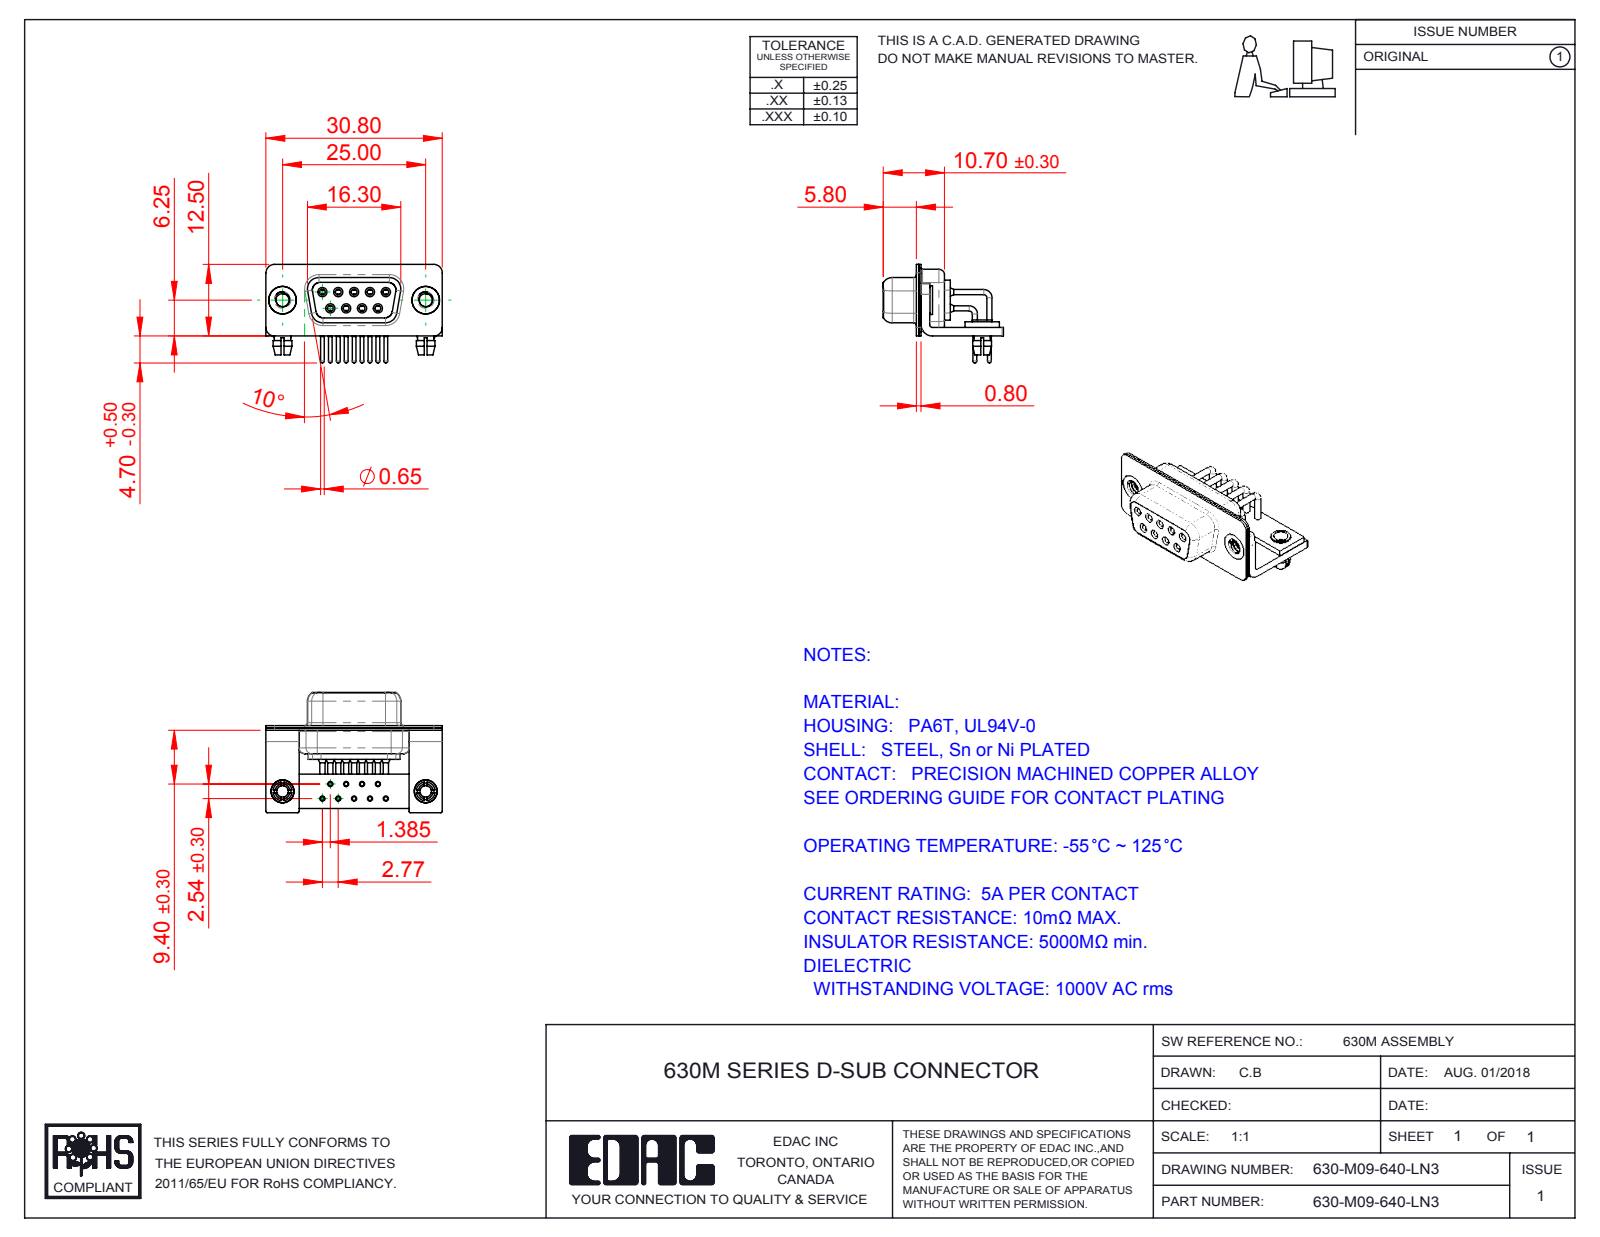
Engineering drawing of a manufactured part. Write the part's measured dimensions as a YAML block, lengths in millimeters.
part_name: "630M Shell Front_09 Contacts; 630M Shell Rear_09 Contacts; 630M Contact Row 1; 630M Contact Row 2 (+6 more)"
step_written_by: "SolidWorks 2016 (CONFIG_CONTROL_DESIGN)"
units: millimeters
bodies: {solids: 19, faces: 916, planar: 276, cylindrical: 416, other: 224}
overall_size: [30.8, 21, 17.2]
volume: 2237
surface_area: 5917
round_holes:
  - {diameter: 2, count: 11}
  - {diameter: 0.9, count: 9}
  - {diameter: 1, count: 9}
  - {diameter: 1.1, count: 9}
  - {diameter: 1.7, count: 9}
  - {diameter: 1.8, count: 9}
  - {diameter: 2.26, count: 2}
  - {diameter: 2.5, count: 2}
  - {diameter: 3.2, count: 2}
  - {diameter: 4, count: 2}
  - {diameter: 4.8, count: 2}
round_bosses_or_shafts:
  - {diameter: 1.6, count: 9}
  - {diameter: 1.5, count: 9}
  - {diameter: 0.9, count: 9}
  - {diameter: 0.65, count: 9}
  - {diameter: 5, count: 2}
  - {diameter: 4.9, count: 2}
  - {diameter: 4, count: 2}
  - {diameter: 3.4, count: 2}
partial_cylinders:
  - {radius: 0.25, count: 16}
  - {radius: 1.5, count: 16}
  - {radius: 2, count: 13}
  - {radius: 1.35, count: 8}
  - {radius: 1.6, count: 8}
  - {radius: 0.5, count: 5}
  - {radius: 0.6, count: 4}
  - {radius: 0.65, count: 4}
face_to_face_distances: [0.4, 0.8, 1.5, 2.3, 1.9, 1, 9.35, 1.45, 2.5, 8.95]
hole_center_spacings: [2.77, 5.54, 3.16, 4.87, 8.31, 2.89, 2.9, 5.03]
